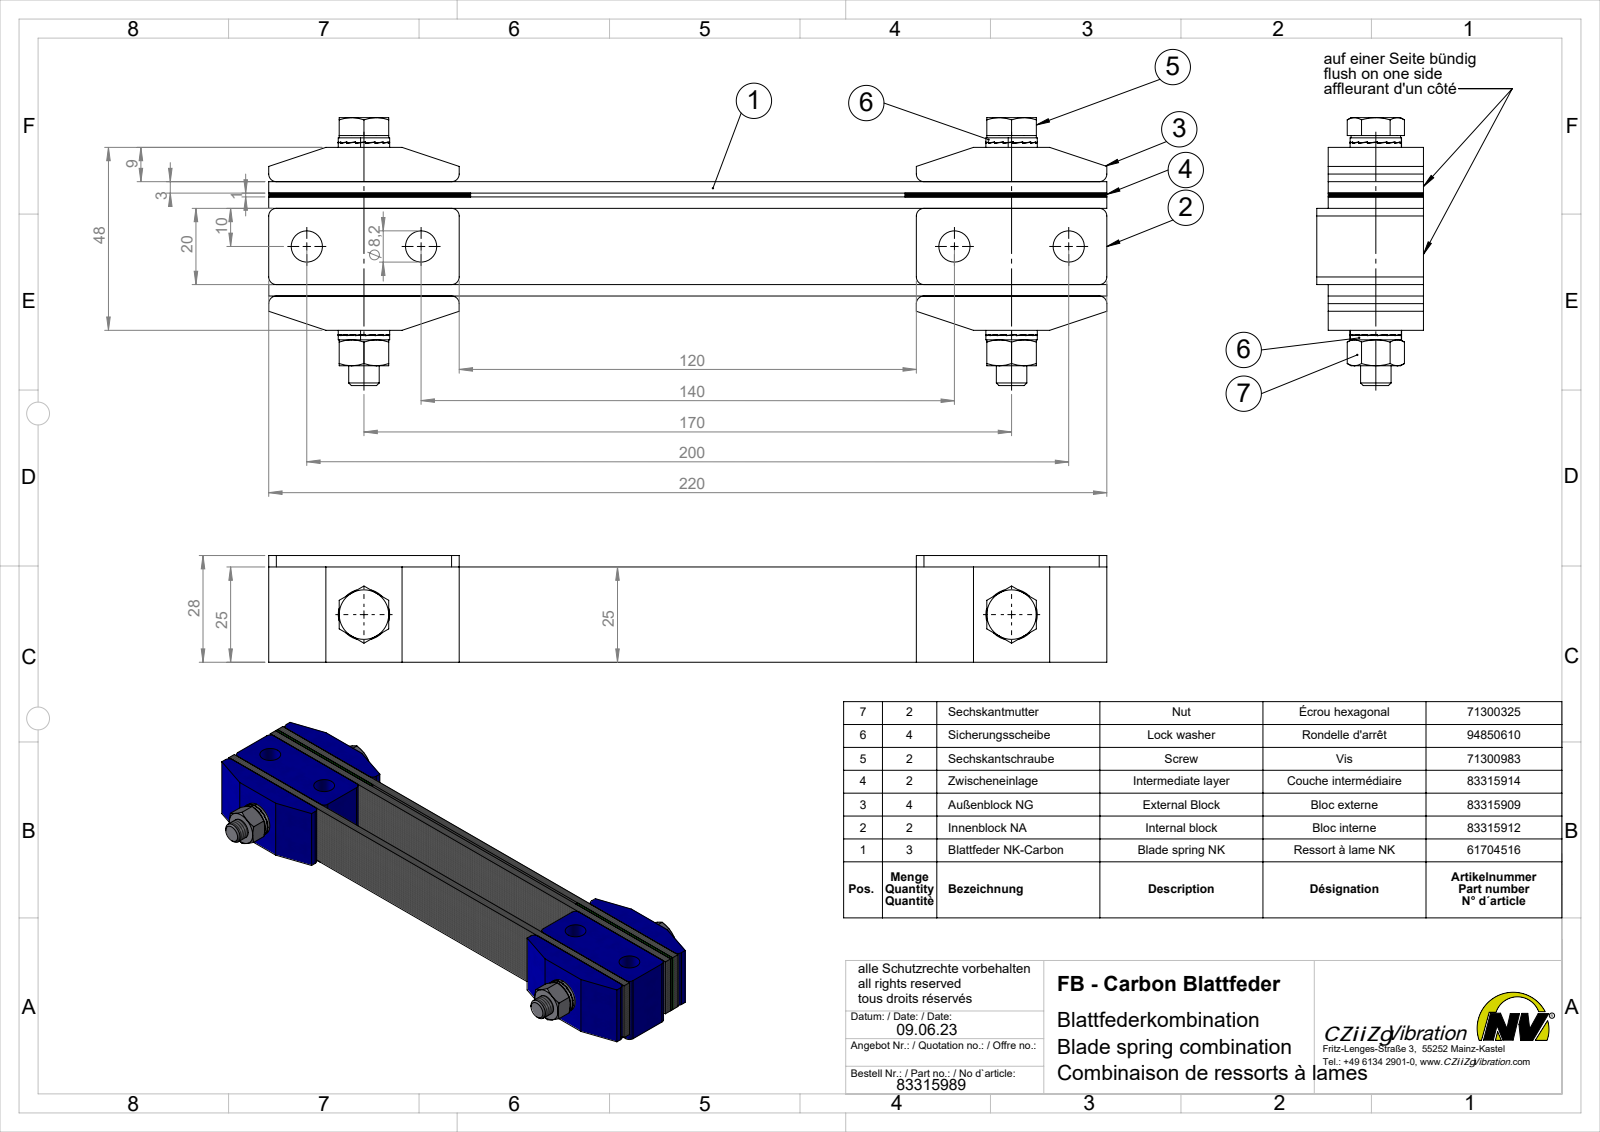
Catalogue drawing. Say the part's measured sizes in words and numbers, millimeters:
The part is named "Blattfederkombination FB #83315989". Its 3-D file was written by "SolidWorks 2022 (AUTOMOTIVE_DESIGN)". It is 19 solids with 720 faces: 576 planar, 92 cylindrical and 52 other. Overall it measures 220 by 70.3 by 28 millimeters. Its volume is 144 592 cubic millimeters and its surface area 78 976 square millimeters. Round holes: 6 of diameter 8.2, 2 of diameter 6.8, 2 of diameter 8, 2 of diameter 8.5, 2 of diameter 8.7. Round bosses or shafts: 2 of diameter 13.5, 2 of diameter 13. Partial cylindrical surfaces (rounded edges, fillets, slot ends): 16 of radius 2. The main face-to-face distances are 3, 4, 23, 27, 1, 24, 20, 7, 30, 26. The hole center spacings are 170, 30, 140, 200.
